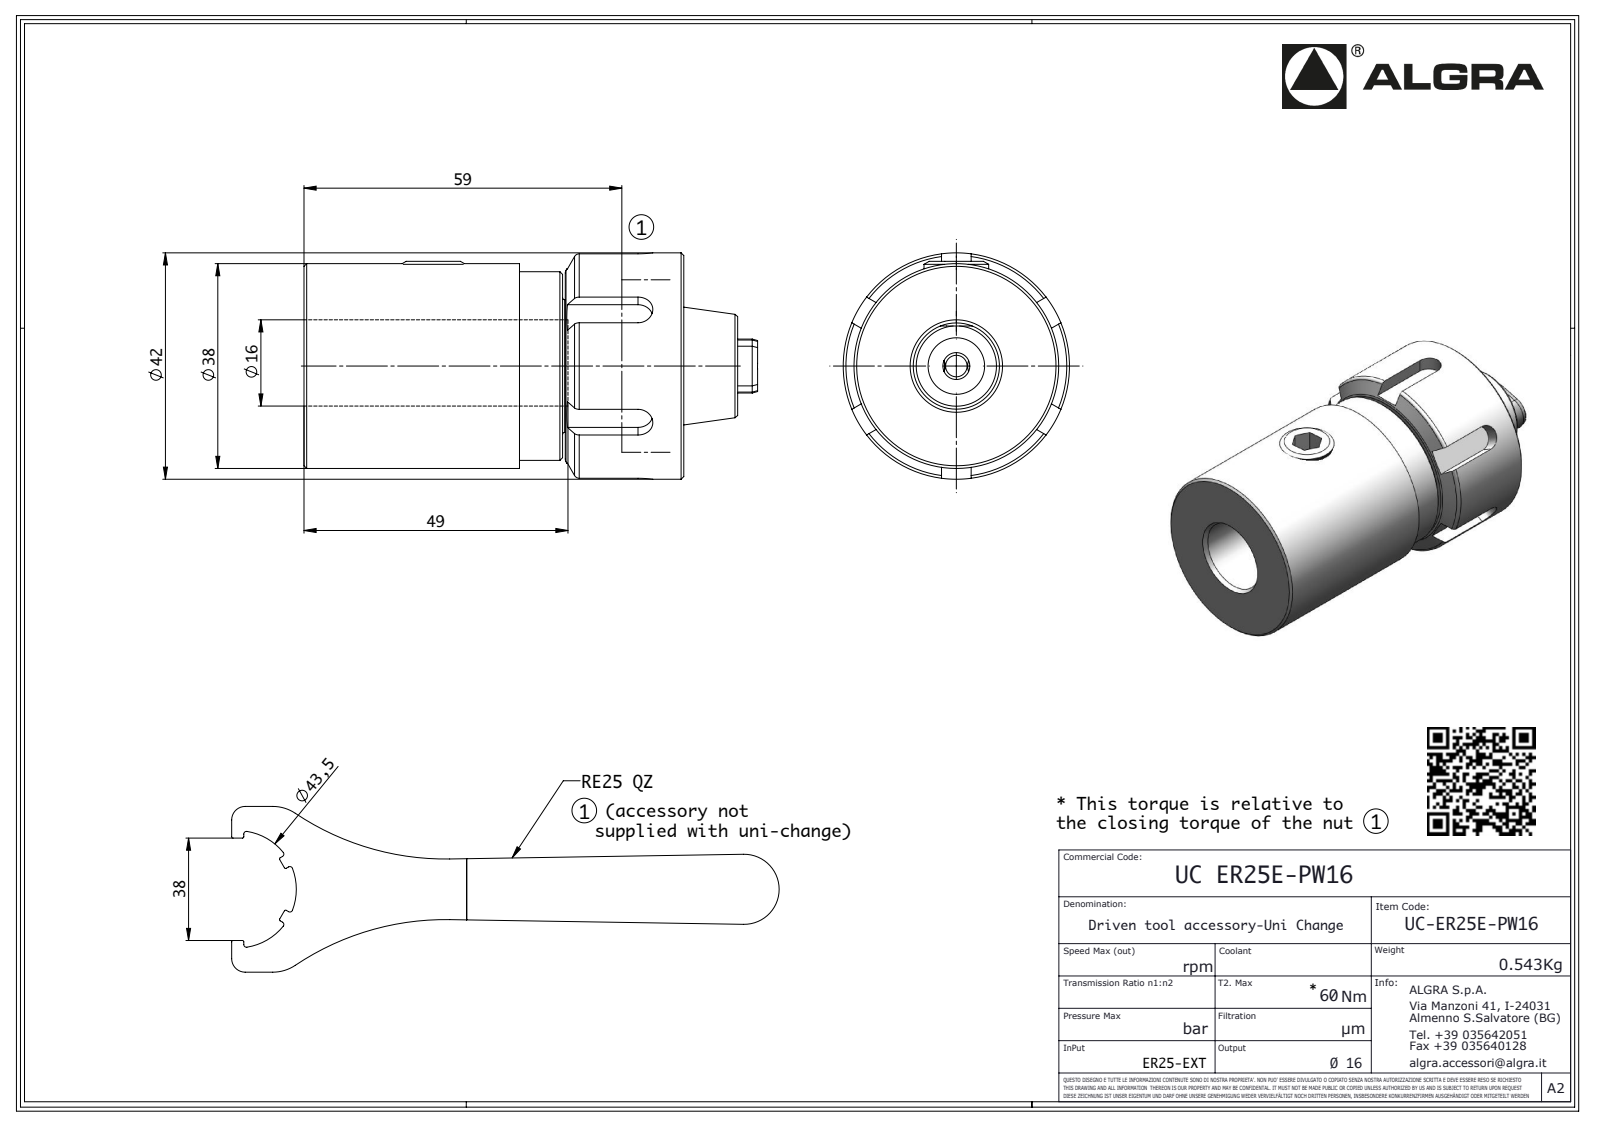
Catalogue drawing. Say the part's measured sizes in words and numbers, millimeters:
The part is named "UCER25E-PW16". Its 3-D file was written by "SolidWorks 2016 (AUTOMOTIVE_DESIGN)". It is 1 solid with 351 faces: 233 planar, 44 cylindrical and 74 other. Overall it measures 84.2 by 42 by 42 millimeters. Its volume is 85 684 cubic millimeters and its surface area 13 633 square millimeters. Round holes: 1 of diameter 2.1. Round bosses or shafts: 1 of diameter 42, 1 of diameter 38, 1 of diameter 35, 1 of diameter 24.6, 1 of diameter 6.37, 1 of diameter 1.7. Partial cylindrical surfaces (rounded edges, fillets, slot ends): 7 of radius 0.33, 7 of radius 0.52, 7 of radius 3.7, 3 of radius 2.75, 2 of radius 3.81, 1 of radius 0.21, 1 of radius 5, 1 of radius 6. The main face-to-face distances are 70.5, 22, 48.5, 0.5, 22.5, 48, 36, 5.5, 30.5, 8.5.
